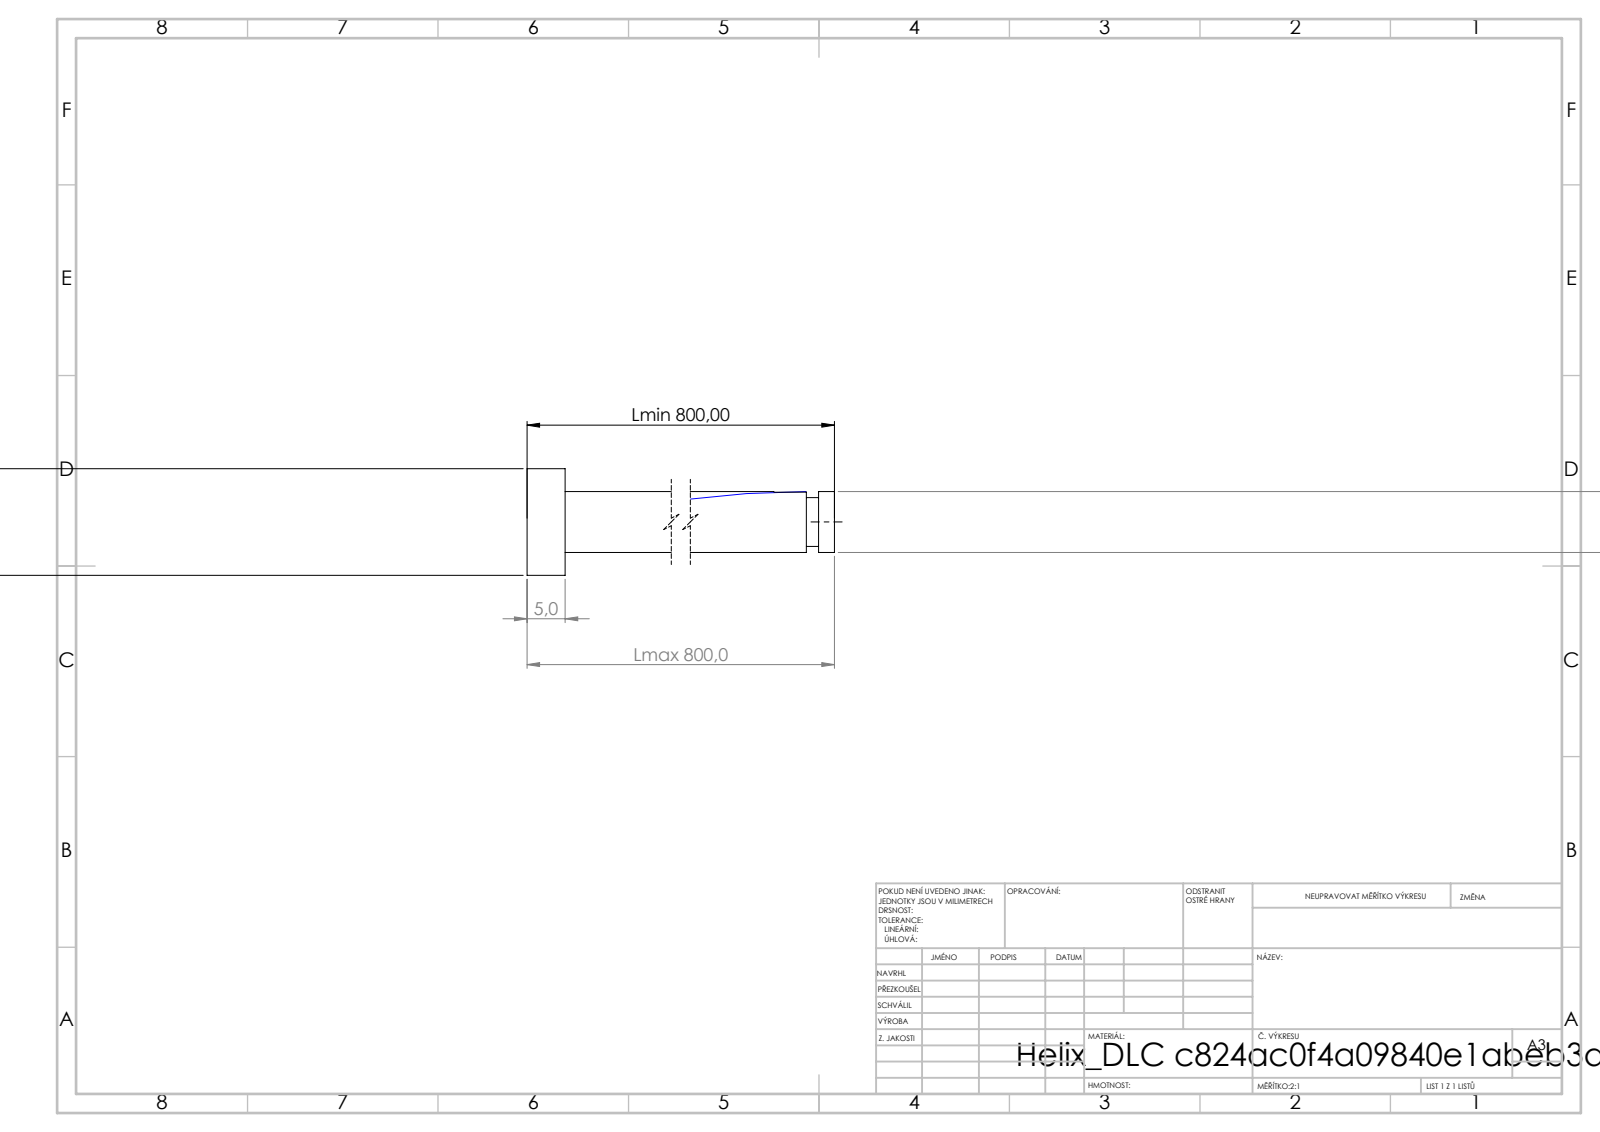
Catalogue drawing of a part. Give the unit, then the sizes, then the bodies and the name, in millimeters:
Units: millimetres
Overall size (bounding box): 800 × 14 × 14
Round bosses / shafts (diameter × count): ⌀14 ×1, ⌀8 ×1, ⌀6.4 ×1
Main face-to-face distances: 5, 800, 795, 797.91, 792.91, 2.09, 796.31, 791.31, 1.6, 3.69
Volume: 49 250 mm³ · Surface area: 27 545 mm²
Bodies: 1 solid, 16 faces (6 planar, 9 cylindrical, 1 other)
STEP written by: SolidWorks 2019 (CONFIG_CONTROL_DESIGN)
